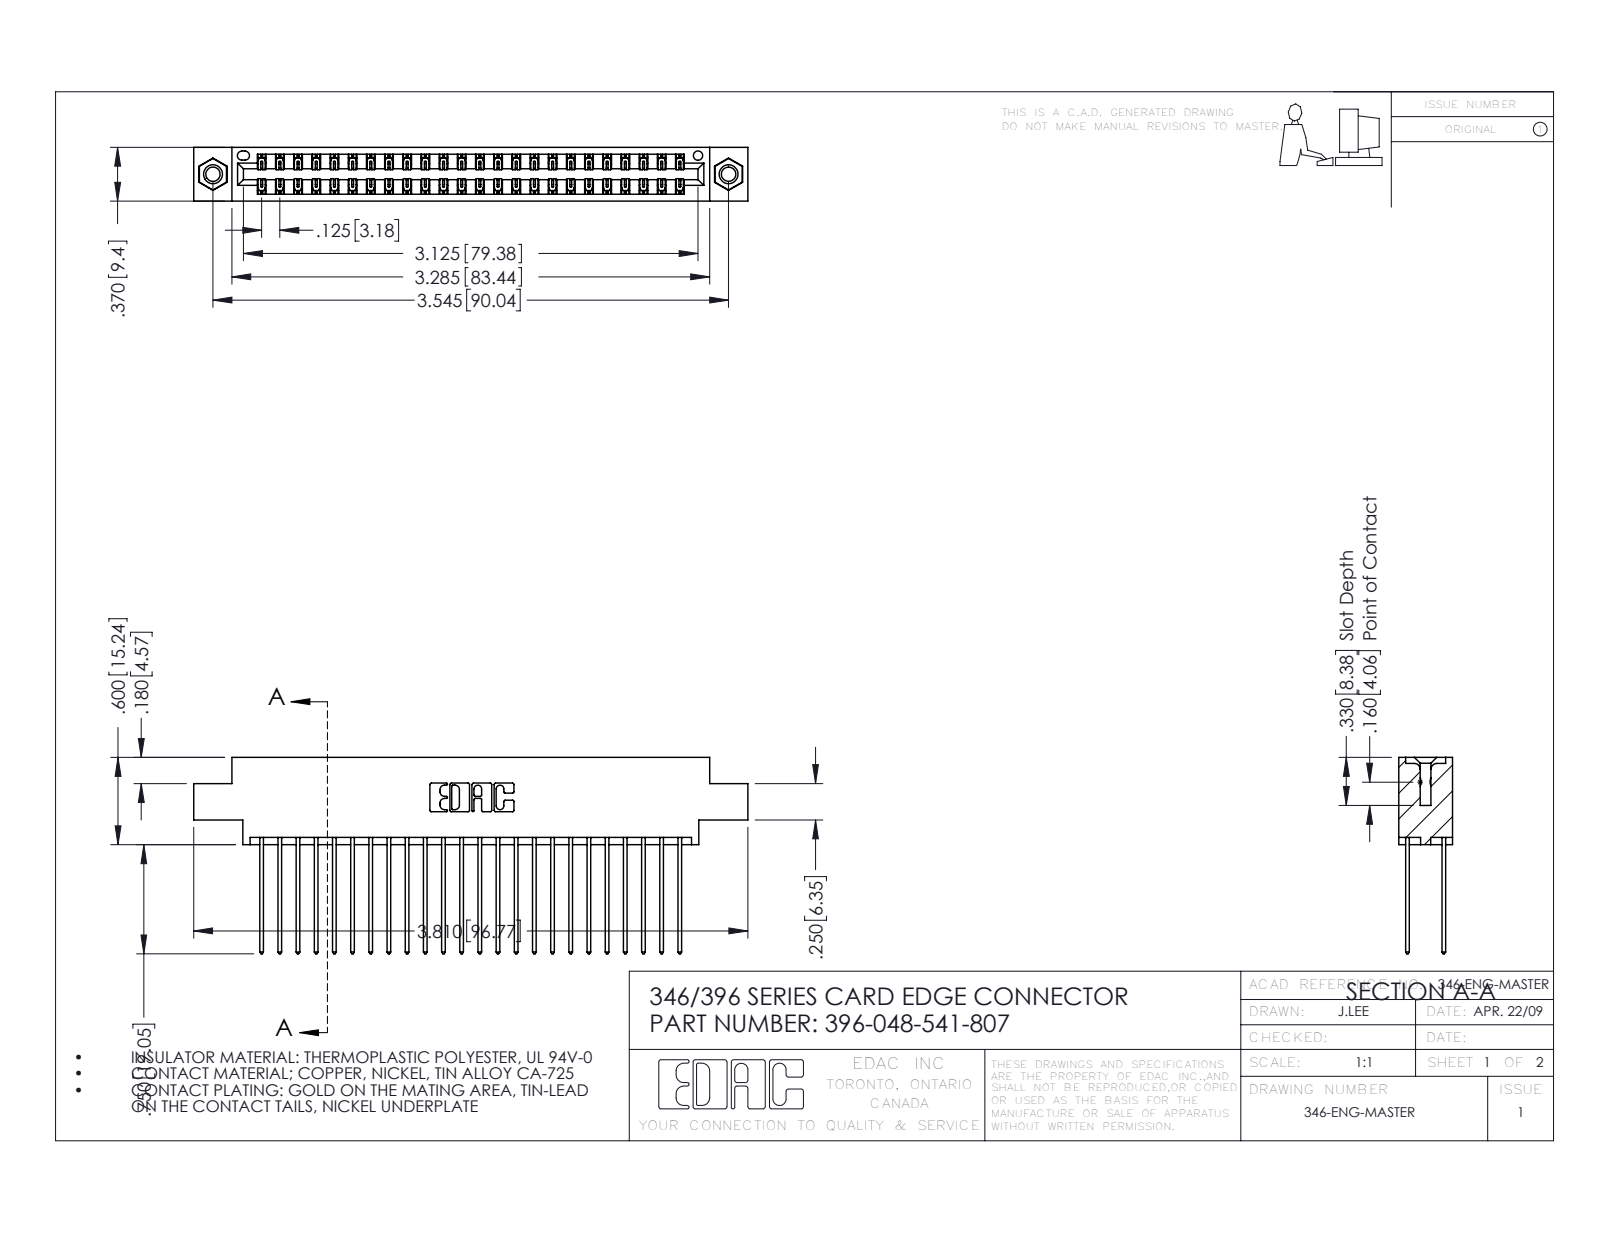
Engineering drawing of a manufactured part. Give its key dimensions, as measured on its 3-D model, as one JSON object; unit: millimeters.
{"part_name": "345-292-001_345-293-141; 345-250-001_345-250-005-103; 346 Part_0.170 Offset - 0.156 Dia-TI; 396-048-541-807", "step_written_by": "SolidWorks 2016 (CONFIG_CONTROL_DESIGN)", "units": "millimeters", "bodies": {"solids": 51, "faces": 2682, "planar": 1792, "cylindrical": 874, "other": 16}, "overall_size": [96.8, 34.3, 9.4], "volume_mm3": 9410, "surface_area_mm2": 14180, "round_holes": [[2.5, 2], [3.2, 2], [4, 2], [1.6, 1]], "round_bosses_or_shafts": [[3.9, 2]], "partial_cylinders_radius": [[0.2, 72], [0.3, 48], [0.3, 22], [0.2, 6], [0.8, 6], [0.7, 3], [0.4, 2], [0.6, 2]], "face_to_face_distances": [1.2, 8.2, 6.4, 1.8, 7.6, 0.6, 9.4, 7, 5.7, 5.6], "hole_center_spacings": [6.2, 84.8, 90]}
